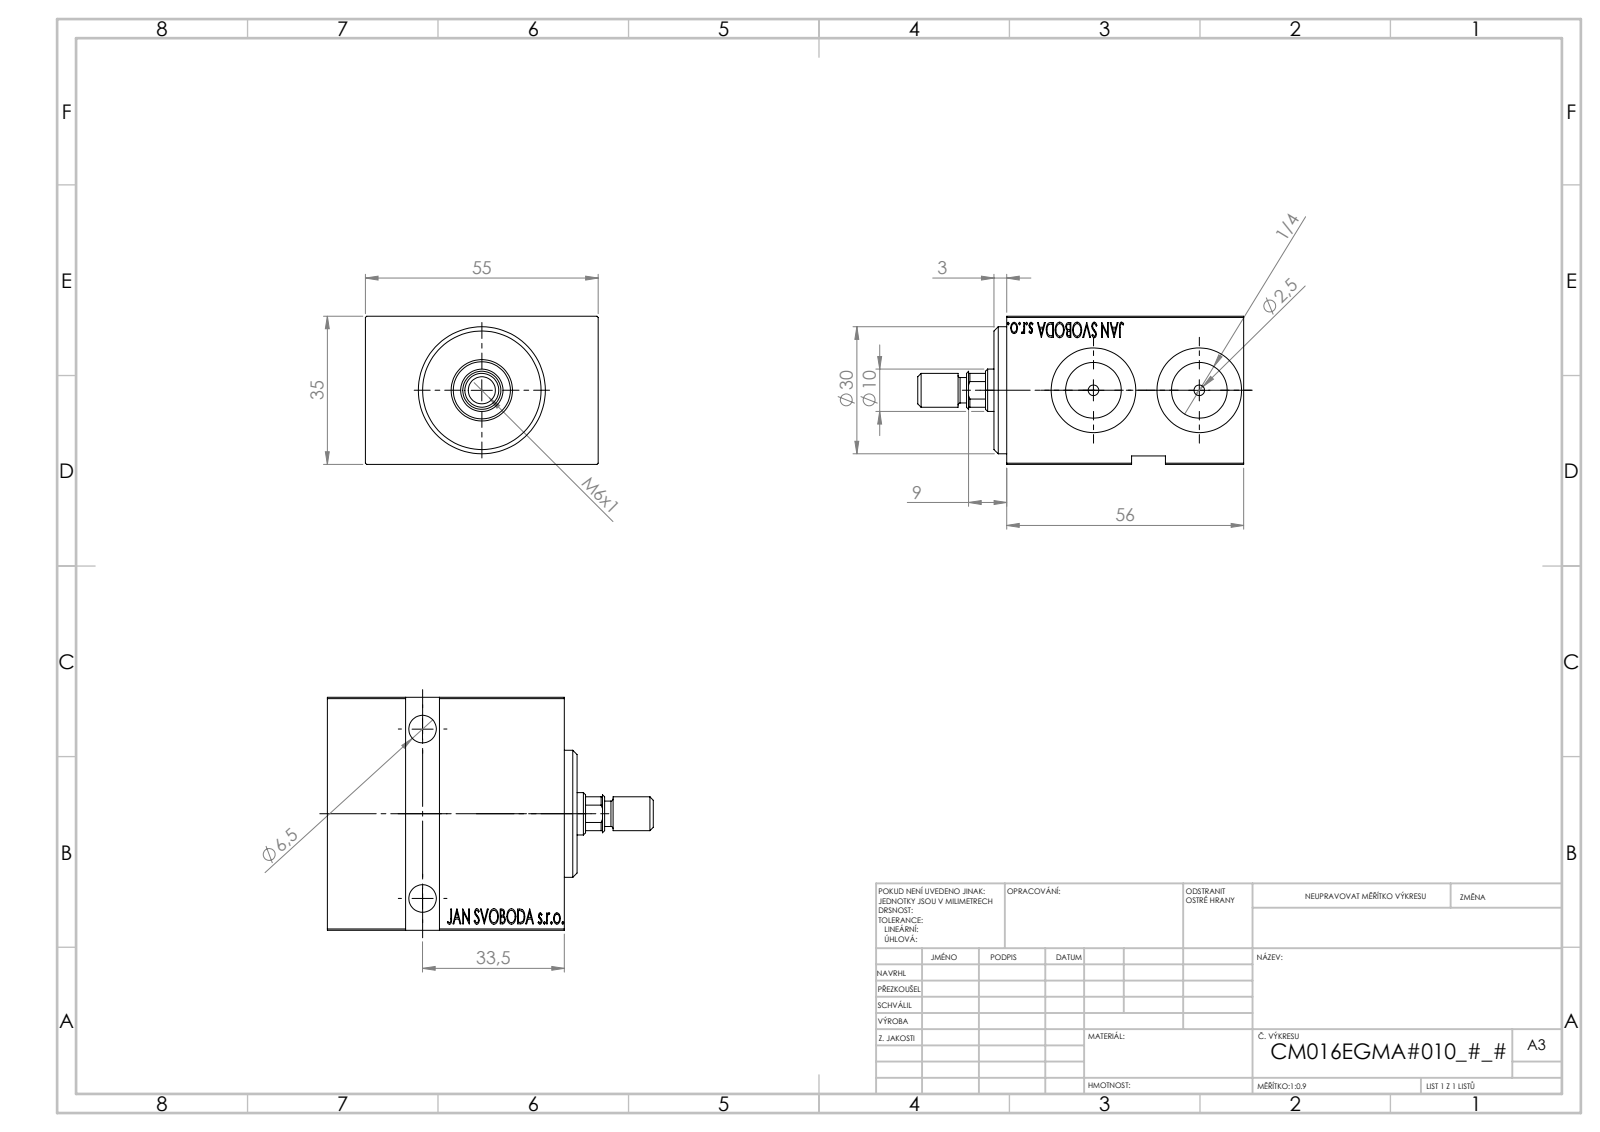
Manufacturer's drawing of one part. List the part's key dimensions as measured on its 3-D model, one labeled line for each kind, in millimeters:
Part name (STEP PRODUCT): V450CM_E_VCP; V450CM_MALE_METRIC; V450CM_VC_B; V450CM_E_Body
STEP written by: SolidWorks 2019 (CONFIG_CONTROL_DESIGN)
Units: millimetres
Bodies: 4 solids, 863 faces (413 planar, 50 cylindrical, 400 other)
Overall size (bounding box): 77 × 55 × 35
Volume: 102 905 mm³ · Surface area: 26 082 mm²
Round holes (diameter × count): ⌀2.5 ×2, ⌀6.5 ×2, ⌀10.5 ×2, ⌀13.16 ×2, ⌀20 ×2, ⌀4.5 ×1, ⌀10 ×1, ⌀13.5 ×1, ⌀14.5 ×1, ⌀16 ×1, ⌀25 ×1
Round bosses / shafts (diameter × count): ⌀30 ×1, ⌀18 ×1, ⌀8 ×1, ⌀6 ×1
Partial cylindrical surfaces — rounded edges, fillets, slot ends (radius × count): R4.5 ×1
Main face-to-face distances: 35, 56, 55, 5, 51, 8, 3, 59, 46, 54
Hole centre spacings: 25, 40
